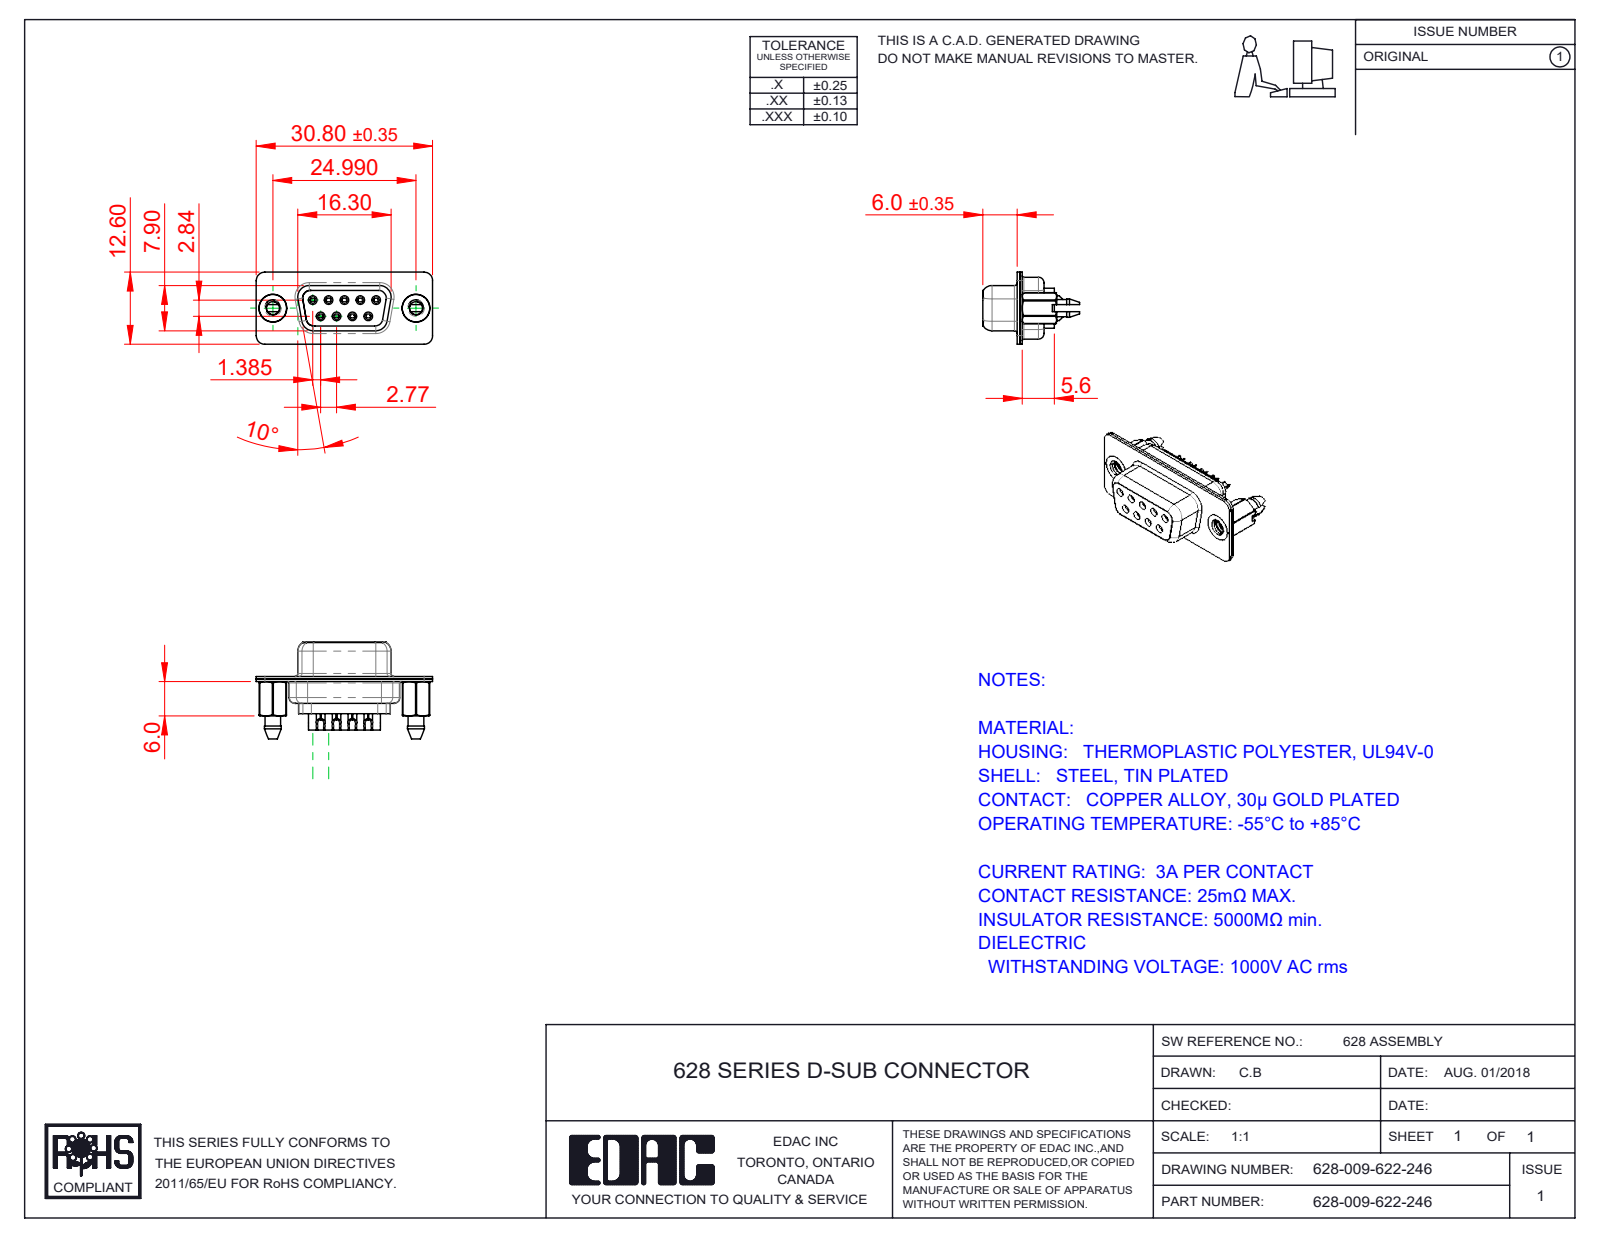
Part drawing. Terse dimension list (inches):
name: 628 Shell Rear_09 Contacts; 628-009-622-246; 628 4-40 Threaded Boardlock_LP; 628 Housing_09 LP (+3 more)
written by: SolidWorks 2020 (CONFIG_CONTROL_DESIGN)
unit: in
bodies: 14 solids, 1154 faces (288 planar, 394 cylindrical, 472 other)
size: 1.213 × 0.665 × 0.496
volume: 0.114 in³; area: 7.465 in²
holes: 9× ⌀0.031, 9× ⌀0.035, 9× ⌀0.043, 9× ⌀0.063, 5× ⌀0.067, 2× ⌀0.089, 2× ⌀0.157, 2× ⌀0.159, 2× ⌀0.191
bosses: 9× ⌀0.079, 9× ⌀0.059, 9× ⌀0.047, 2× ⌀0.195, 2× ⌀0.189
rounds: 19× R0.059, 12× R0.079, 9× R0.011, 6× R0.039, 6× R0.053, 6× R0.063, 4× R0.01, 4× R0.02
face distances: 0.018, 0.016, 0.035, 0.075, 0.335, 0.26, 0.055, 0.02, 0.256, 0.492
hole spacings: 0.124, 0.109, 0.218, 0.198, 0.198, 0.327, 0.294, 0.295
